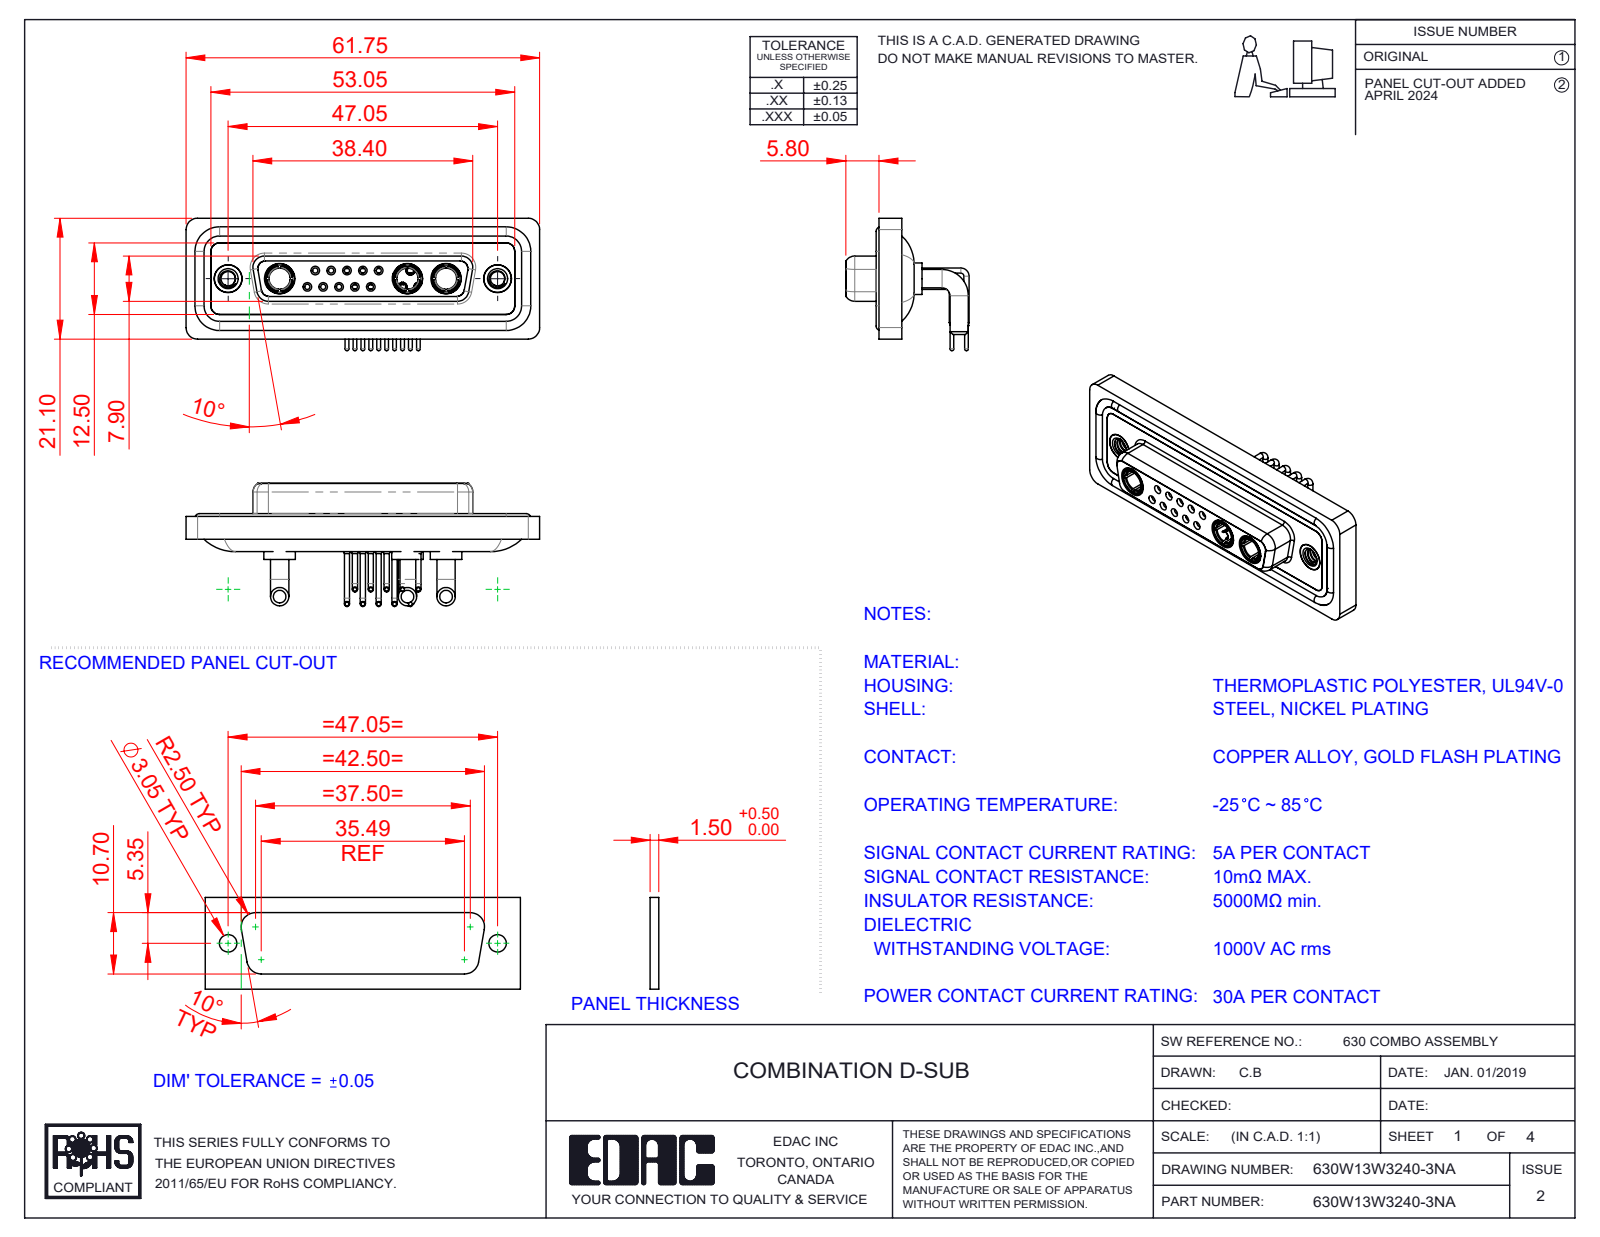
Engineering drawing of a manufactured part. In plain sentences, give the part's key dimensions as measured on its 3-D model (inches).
The part is named "630Combo Contact Row 2_50 Contacts; 630Combo Contact Row 1_50 Contacts; 630Combo Threaded Rivet_A; 630W13W3240-3NA (+5 more)". Its 3-D file was written by "SolidWorks 2023 (CONFIG_CONTROL_DESIGN)". It is 23 solids with 1144 faces: 342 planar, 491 cylindrical and 311 other. Overall it measures 2.431 by 0.91 by 0.848 inches. Its volume is 0.522 cubic inches and its surface area 22.25 square inches. Round holes: 10 of diameter 0.035, 10 of diameter 0.043, 10 of diameter 0.059, 10 of diameter 0.079, 5 of diameter 0.063, 5 of diameter 0.067, 5 of diameter 0.191, 3 of diameter 0.146, 3 of diameter 0.209, 2 of diameter 0.098, 2 of diameter 0.157, 2 of diameter 0.159. Round bosses or shafts: 15 of diameter 0.035, 12 of diameter 0.063, 10 of diameter 0.026, 6 of diameter 0.126, 5 of diameter 0.079, 5 of diameter 0.059, 3 of diameter 0.217, 3 of diameter 0.205. Partial cylindrical surfaces (rounded edges, fillets, slot ends): 18 of radius 0.059, 18 of radius 0.079, 8 of radius 0.053, 8 of radius 0.063, 4 of radius 0.01, 4 of radius 0.02, 4 of radius 0.024, 4 of radius 0.026. The main face-to-face distances are 0.016, 0.071, 0.161, 0.043, 0.063, 0.122, 0.059, 0.098, 0.146, 0.055. The hole center spacings are 0.124, 0.109, 0.218, 0.198, 0.327, 0.198, 0.295, 0.436.
